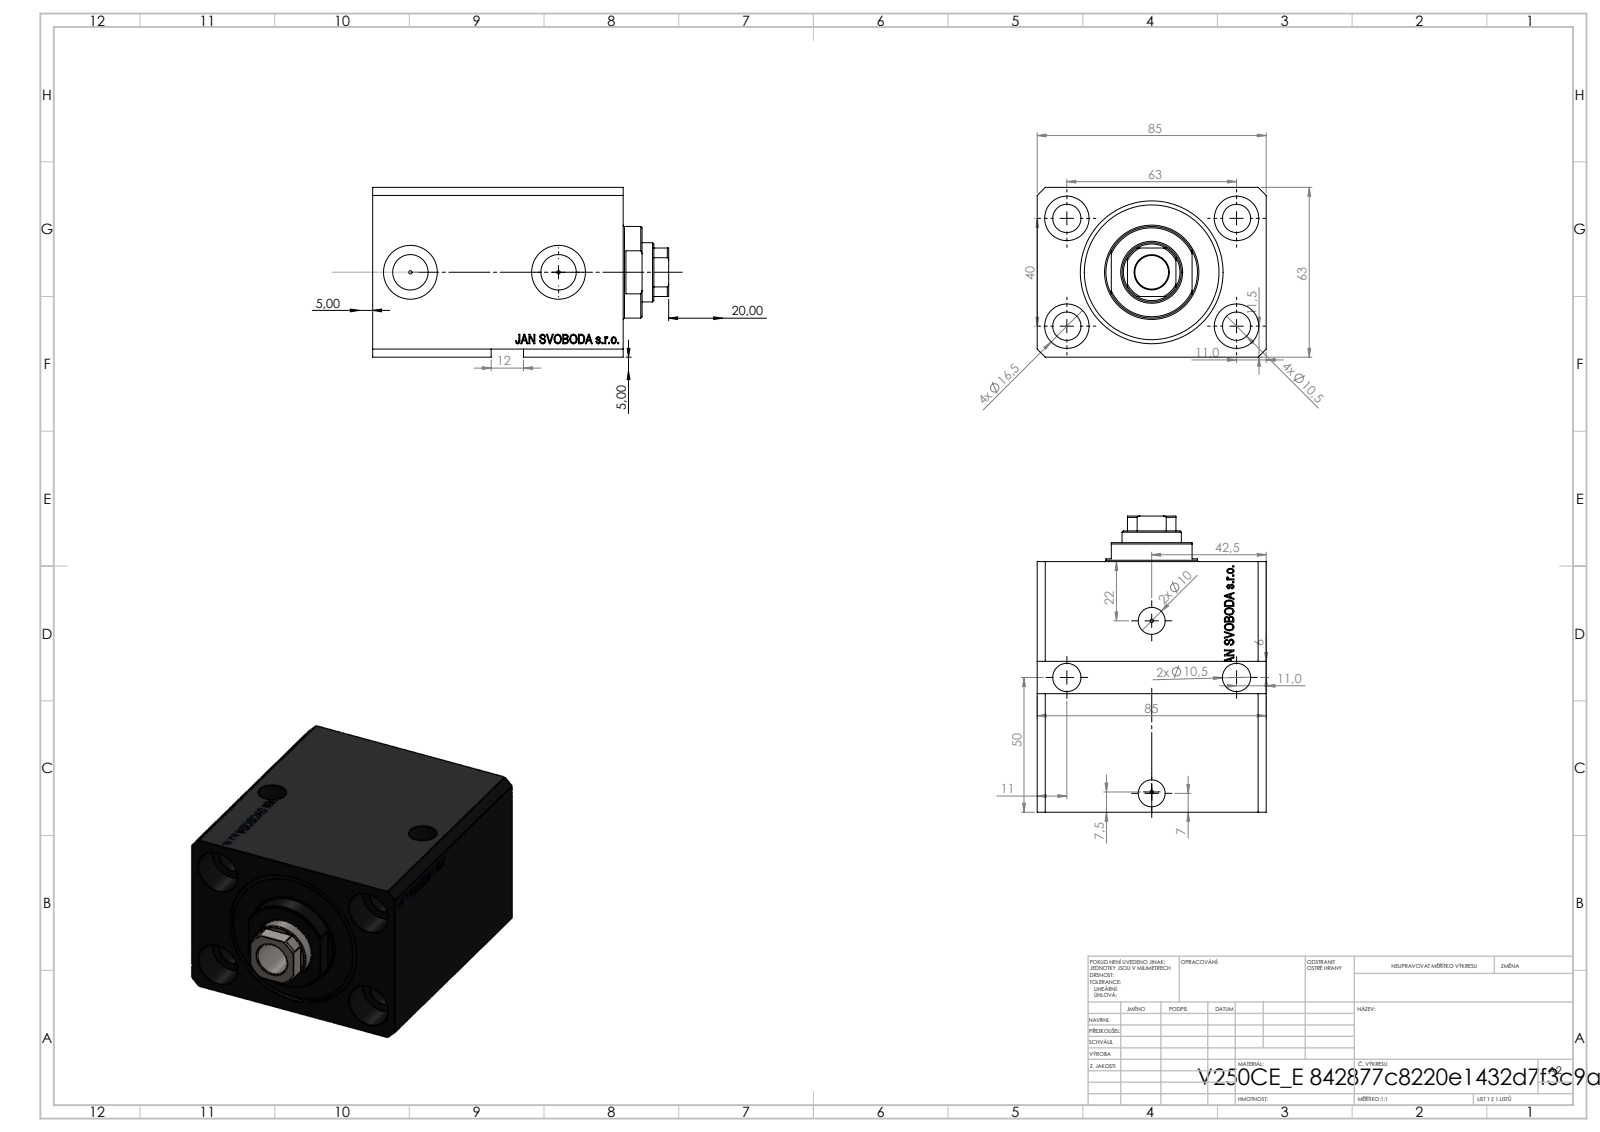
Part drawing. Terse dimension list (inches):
name: V250CE_C_VCP; V250CE_VC_E; V250CE_E_Body
written by: SolidWorks 2019 (CONFIG_CONTROL_DESIGN)
unit: in
bodies: 3 solids, 917 faces (459 planar, 84 cylindrical, 374 other)
size: 4.327 × 3.346 × 2.48
volume: 26.07 in³; area: 138.6 in²
holes: 6× ⌀0.413, 4× ⌀0.049, 4× ⌀0.65, 2× ⌀0.394, 2× ⌀0.518, 2× ⌀0.787, 1× ⌀0.492, 1× ⌀0.866, 1× ⌀1.575, 1× ⌀2.087
bosses: 1× ⌀1.339
rounds: 1× R0.413
face distances: 2.48, 3.346, 3.661, 2.594, 1.067, 0.449, 2.146, 3.213, 0.433, 3.228
hole spacings: 1.469, 2.48, 1.491, 1.575, 2.082, 2.098, 2.938, 0.021
